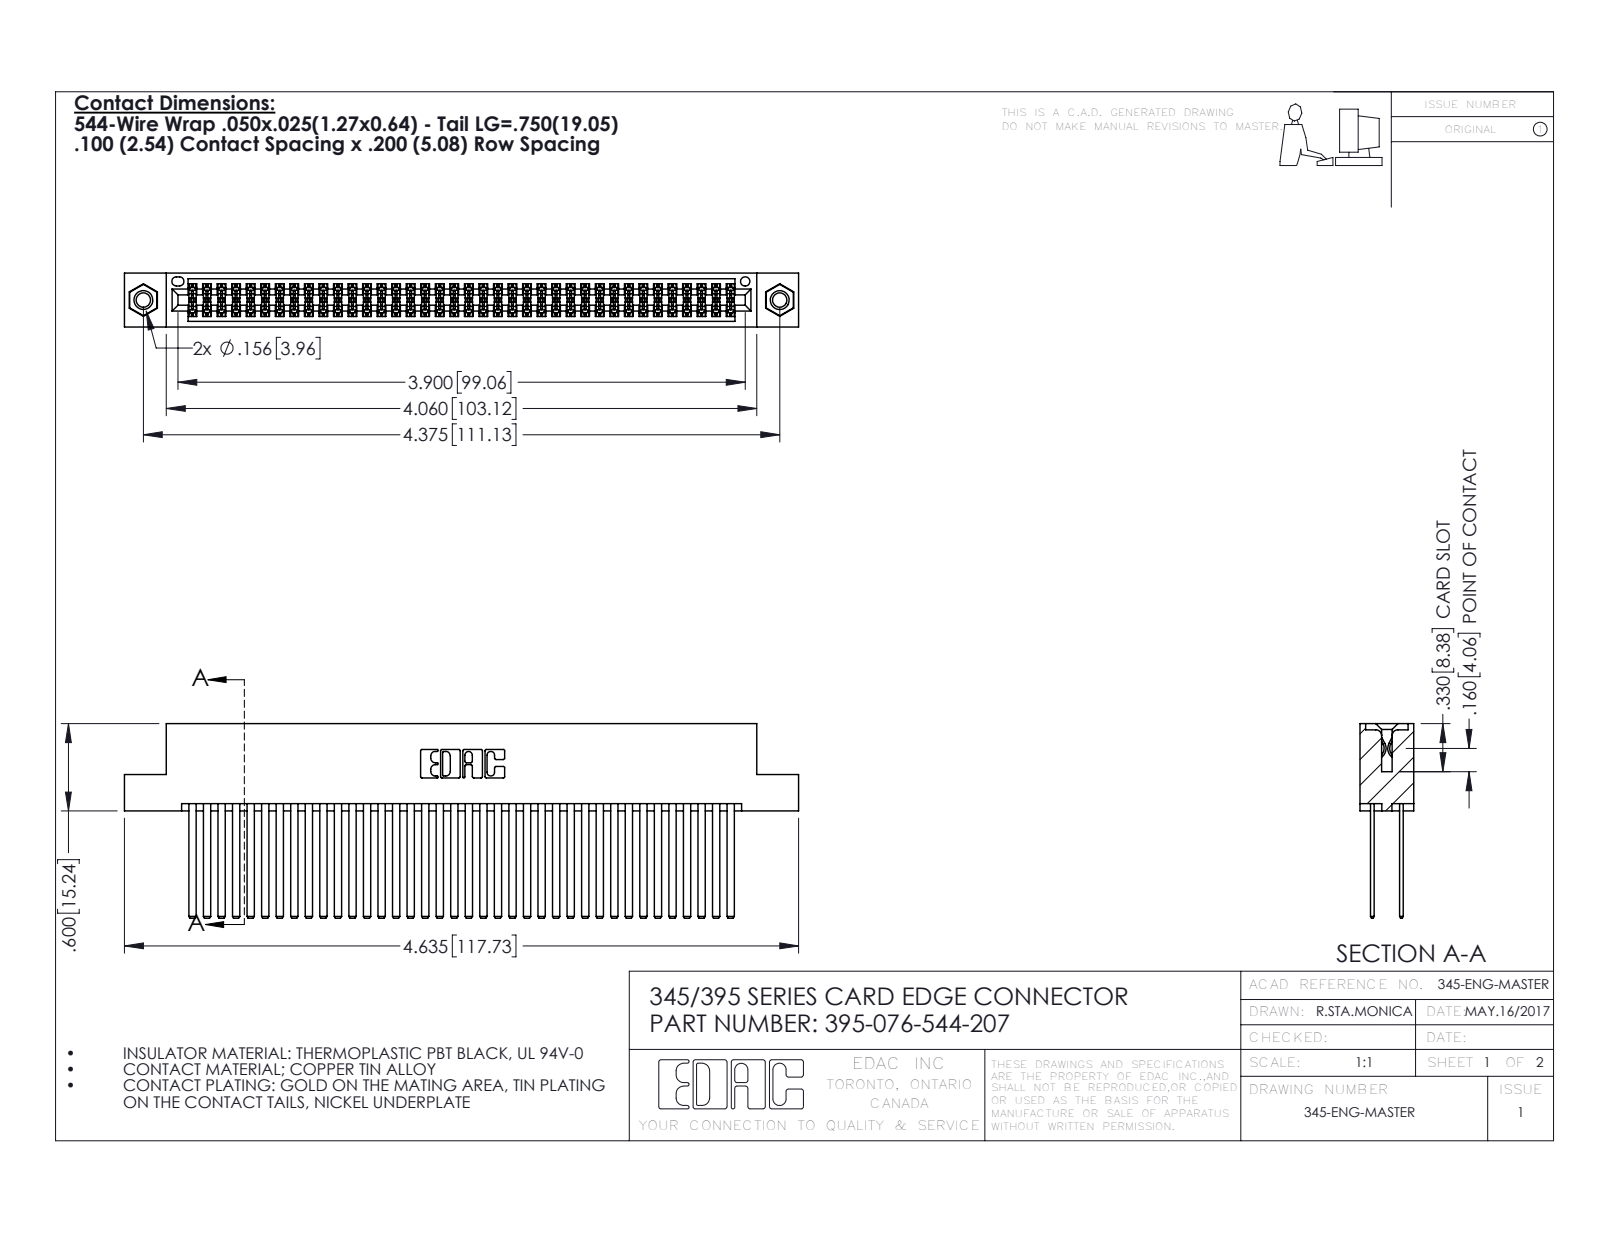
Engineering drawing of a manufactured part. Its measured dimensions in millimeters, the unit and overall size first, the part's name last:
Units: millimetres
Overall size (bounding box): 117.7 × 34 × 9.4
Round holes (diameter × count): ⌀2.5 ×2, ⌀3.2 ×2, ⌀4 ×2, ⌀1.6 ×1
Round bosses / shafts (diameter × count): ⌀3.9 ×2
Partial cylindrical surfaces — rounded edges, fillets, slot ends (radius × count): R0.2 ×114, R0.3 ×22, R0.2 ×6, R0.8 ×6, R0.7 ×3, R0.4 ×2, R0.5 ×2, R0.6 ×2
Main face-to-face distances: 5.1, 0.6, 1.8, 2.5, 6.9, 7.6, 5.7, 4.4, 9.4, 1.3
Hole centre spacings: 6.9, 105.1, 111.1
Volume: 12 500 mm³ · Surface area: 21 480 mm²
Bodies: 79 solids, 3530 faces (2316 planar, 1198 cylindrical, 16 other)
Part name (STEP PRODUCT): 345-250-001_345-250-005-103; 345-292-001_345-293-144; 345 Part_Flush Mounting Lugs - 0.156 Dia-TI; 395-076-544-207
STEP written by: SolidWorks 2016 (CONFIG_CONTROL_DESIGN)
